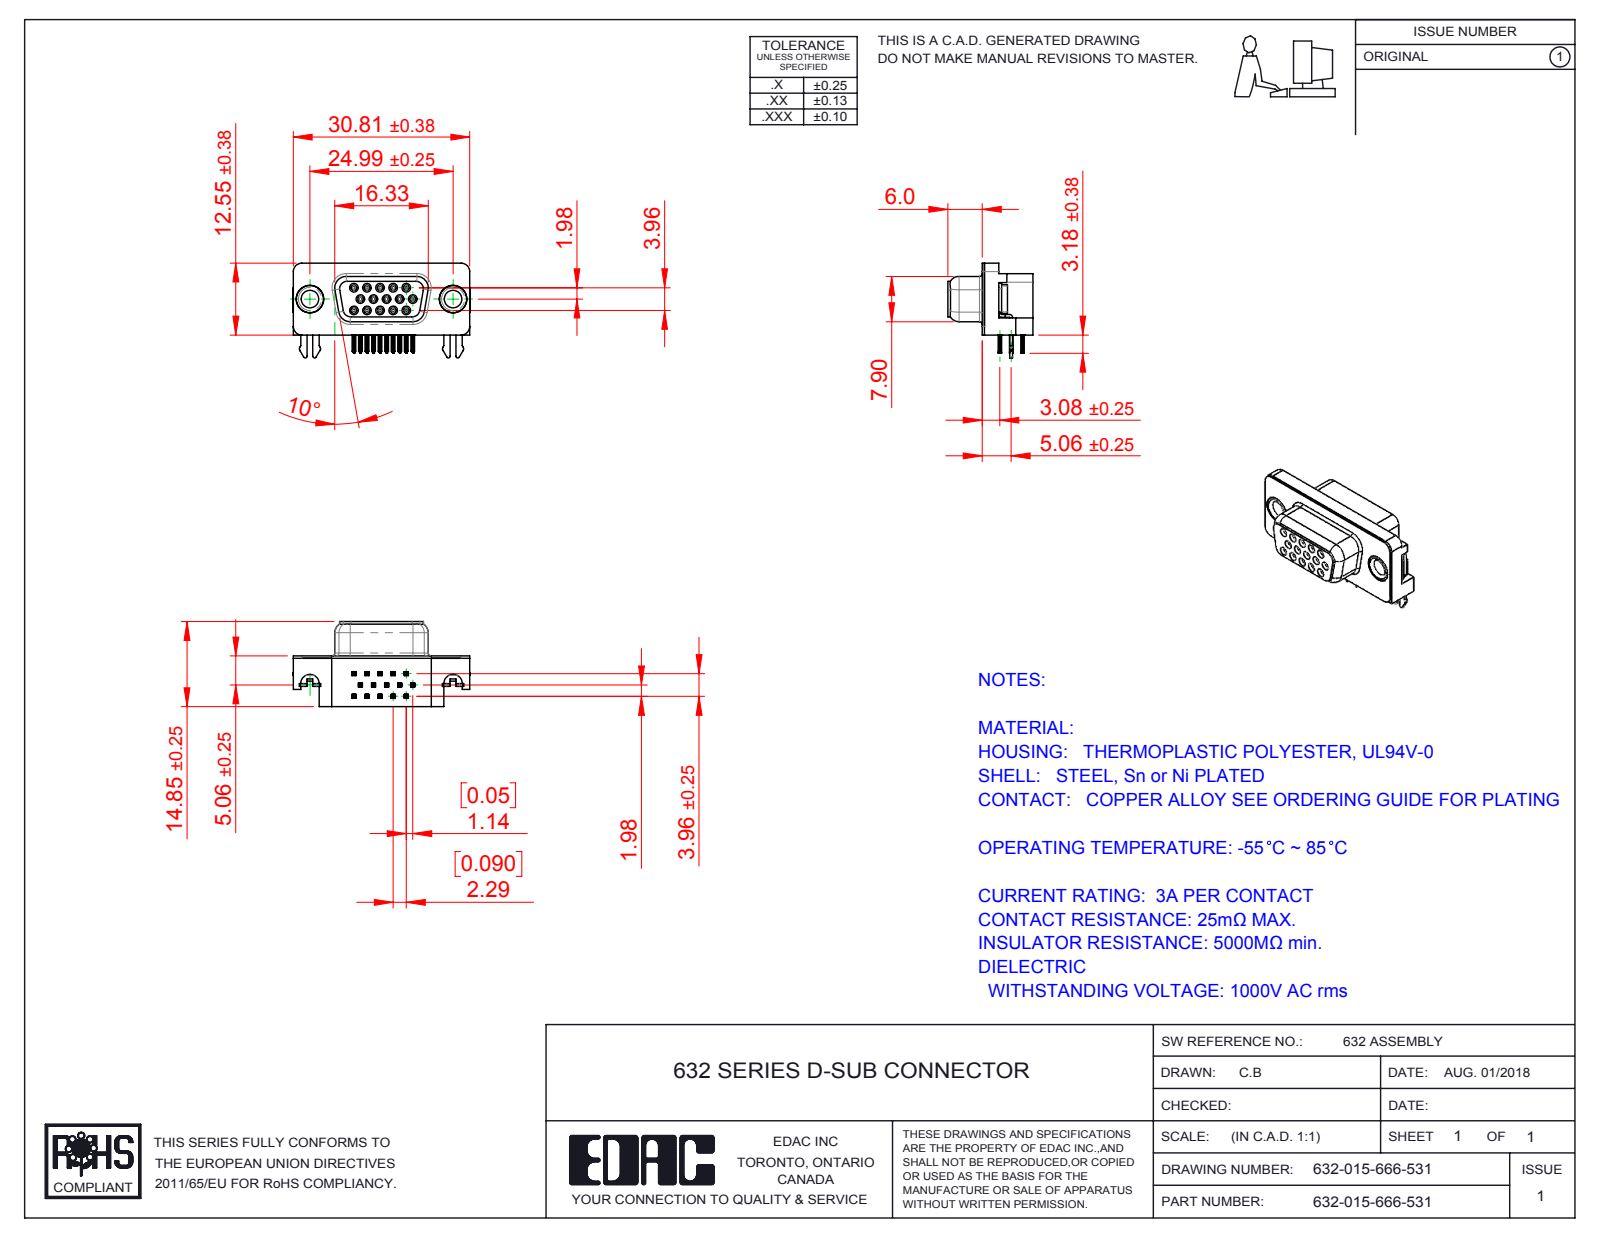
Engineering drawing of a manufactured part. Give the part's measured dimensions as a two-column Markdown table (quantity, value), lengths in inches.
| quantity | value |
| --- | --- |
| part name | 632-015-666-501; 632 Contact Middle; 632 Housing_15 Socket; 632 2 Prong Board Lock (+4 more) |
| STEP written by | SolidWorks 2016 (CONFIG_CONTROL_DESIGN) |
| units | inches |
| bodies | 21 solids, 2298 faces (990 planar, 594 cylindrical, 714 other) |
| overall size | 1.216 × 0.652 × 0.585 |
| volume | 0.177 in³ |
| surface area | 7.741 in² |
| round holes (diameter × count) | 0.031 × 15, 0.035 × 15, 0.12 × 2, 0.157 × 2, 0.189 × 2, 0.197 × 2 |
| round bosses / shafts (diameter × count) | 0.047 × 15, 0.193 × 2, 0.187 × 2, 0.152 × 2 |
| partial cylindrical surfaces (radius × count) | 0.004 × 120, 0.006 × 60, 0.014 × 30, 0.013 × 15, 0.039 × 11, 0.011 × 10, 0.02 × 10, 0.01 × 8 |
| main face-to-face distances | 0.016, 0.078, 0.333, 0.348, 0.114, 0.098, 0.234, 0.252, 0.264, 0.278 |
| hole center spacings | 0.09, 0.09, 0.156, 0.18, 0.238, 0.156, 0.18, 0.27 |
